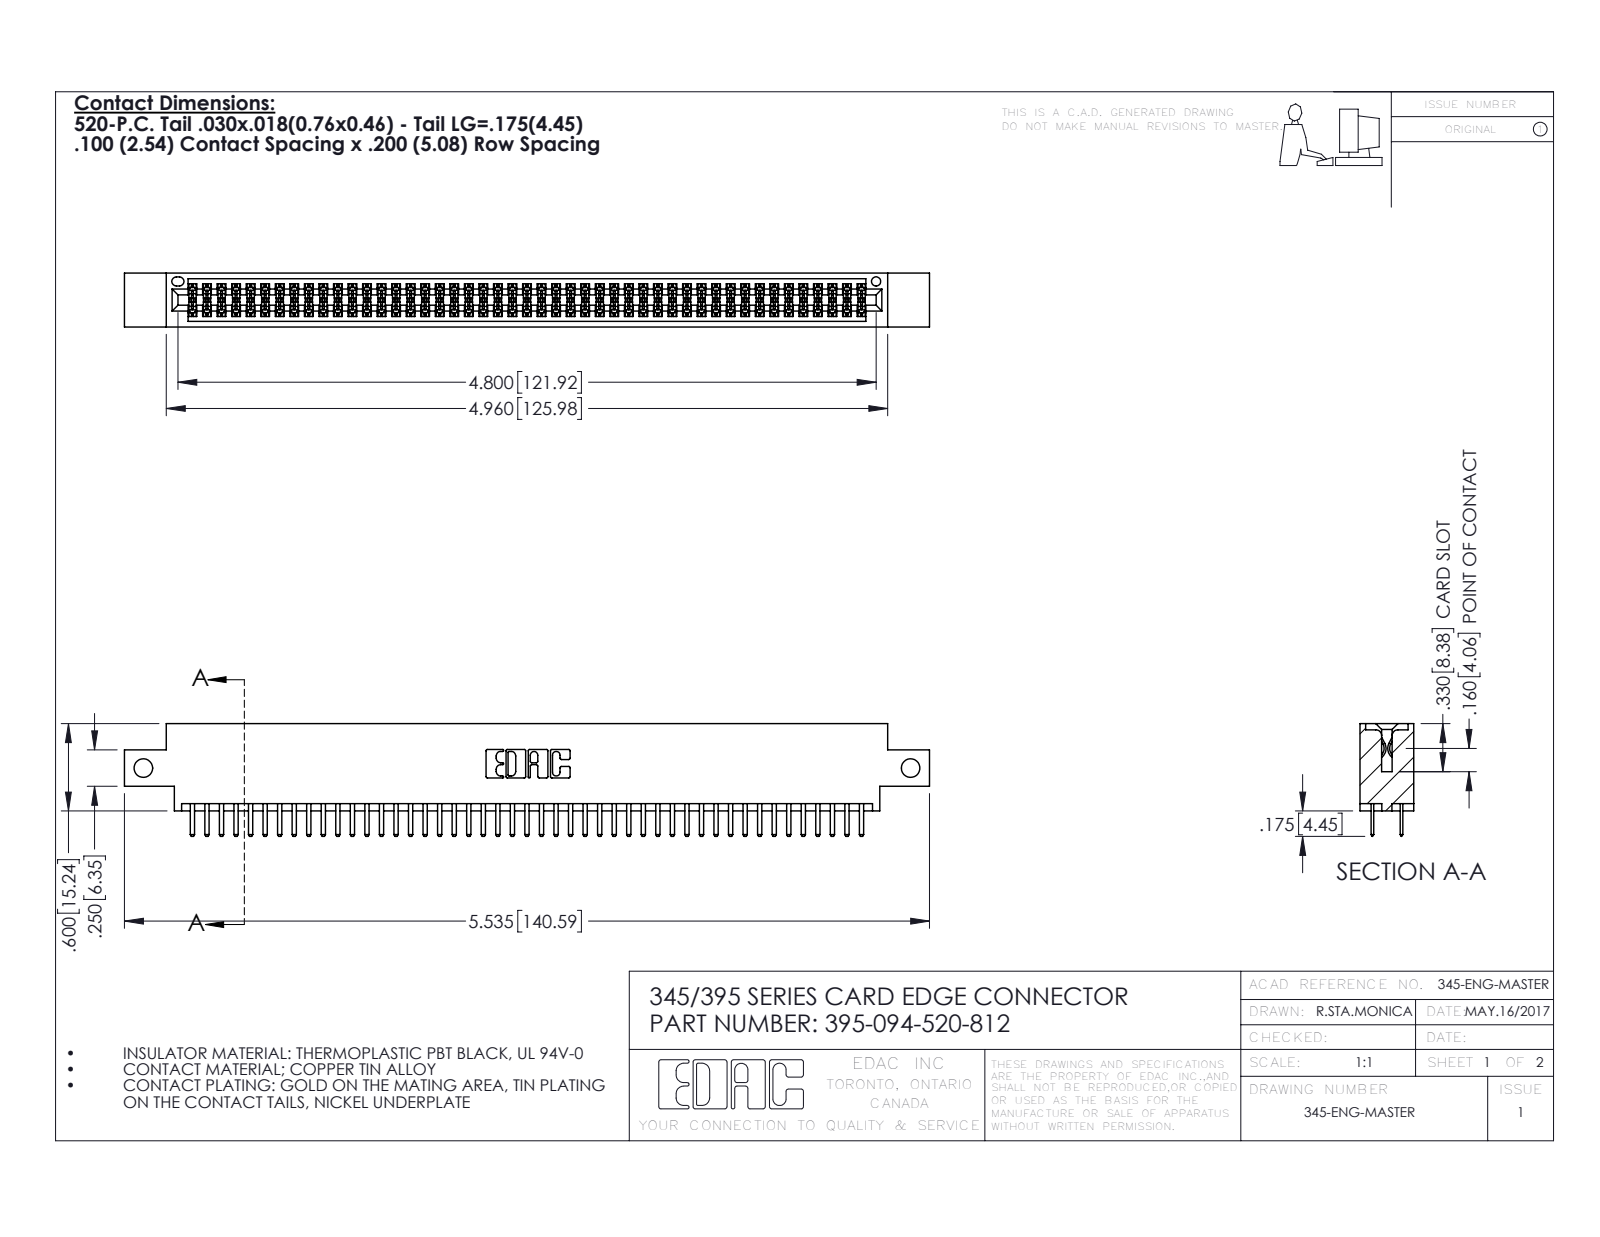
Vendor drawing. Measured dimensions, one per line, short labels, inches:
name: 345-292-001_345-293-120; 395-094-520-812; 345 Part_0.170 Offset - Side Mount
written by: SolidWorks 2016 (CONFIG_CONTROL_DESIGN)
unit: in
bodies: 95 solids, 5206 faces (3374 planar, 1832 cylindrical, 0 other)
size: 5.535 × 0.775 × 0.37
volume: 0.821 in³; area: 30.87 in²
holes: 2× ⌀0.128, 1× ⌀0.064
rounds: 141× R0.006, 98× R0.01, 22× R0.01, 6× R0.007, 6× R0.031, 3× R0.026, 2× R0.014, 2× R0.019
face distances: 0.298, 0.072, 0.2, 0.37, 0.098, 0.272, 0.025, 0.225, 0.022, 0.175
hole spacings: 5.275
